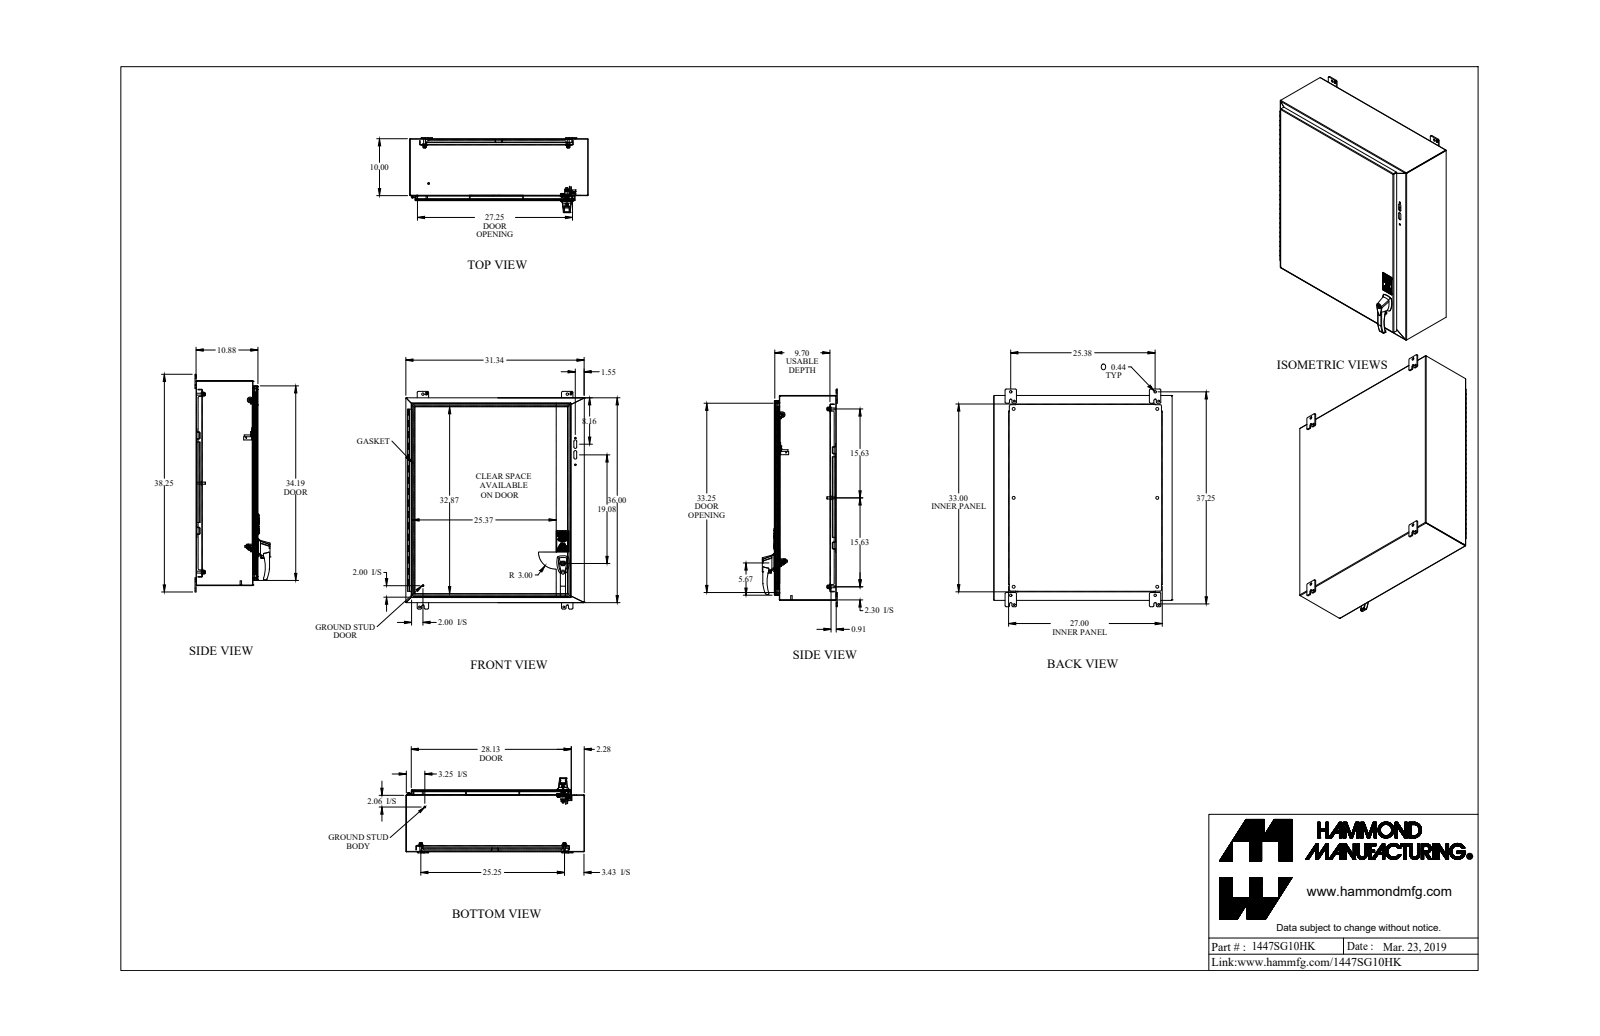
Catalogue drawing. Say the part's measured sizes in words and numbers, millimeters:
The part is named "1447SG10HK". Its 3-D file was written by "SolidWorks 2019 (AUTOMOTIVE_DESIGN)". It is 58 solids with 1381 faces: 849 planar, 409 cylindrical and 123 other. Overall it measures 971.54 by 796.93 by 334.7 millimeters. Its volume is 6 865 000 cubic millimeters and its surface area 6 879 000 square millimeters. Round holes: 6 of diameter 12.7, 5 of diameter 7.94, 4 of diameter 4.47, 4 of diameter 7.81, 4 of diameter 11.11, 4 of diameter 11.3, 2 of diameter 3.97, 2 of diameter 4.39, 2 of diameter 5.46, 2 of diameter 6.35, 2 of diameter 6.73, 2 of diameter 7.14. Round bosses or shafts: 10 of diameter 9.53, 7 of diameter 6.35, 6 of diameter 25.4, 6 of diameter 16.51, 6 of diameter 8.38, 4 of diameter 3.97, 2 of diameter 12.7, 2 of diameter 10.21. Partial cylindrical surfaces (rounded edges, fillets, slot ends): 32 of radius 4.76, 28 of radius 2, 20 of radius 6.35, 16 of radius 0.17, 13 of radius 3.17, 12 of radius 2.93, 10 of radius 0.76, 8 of radius 3.83. The main face-to-face distances are 1.83, 274.4, 272.57, 276.23, 2.41, 248.19, 246.36, 26.21, 28.04, 250.6. The hole center spacings are 641.35, 396.88, 644.53, 754.22, 28.21, 44.08, 44.09, 47.12.
